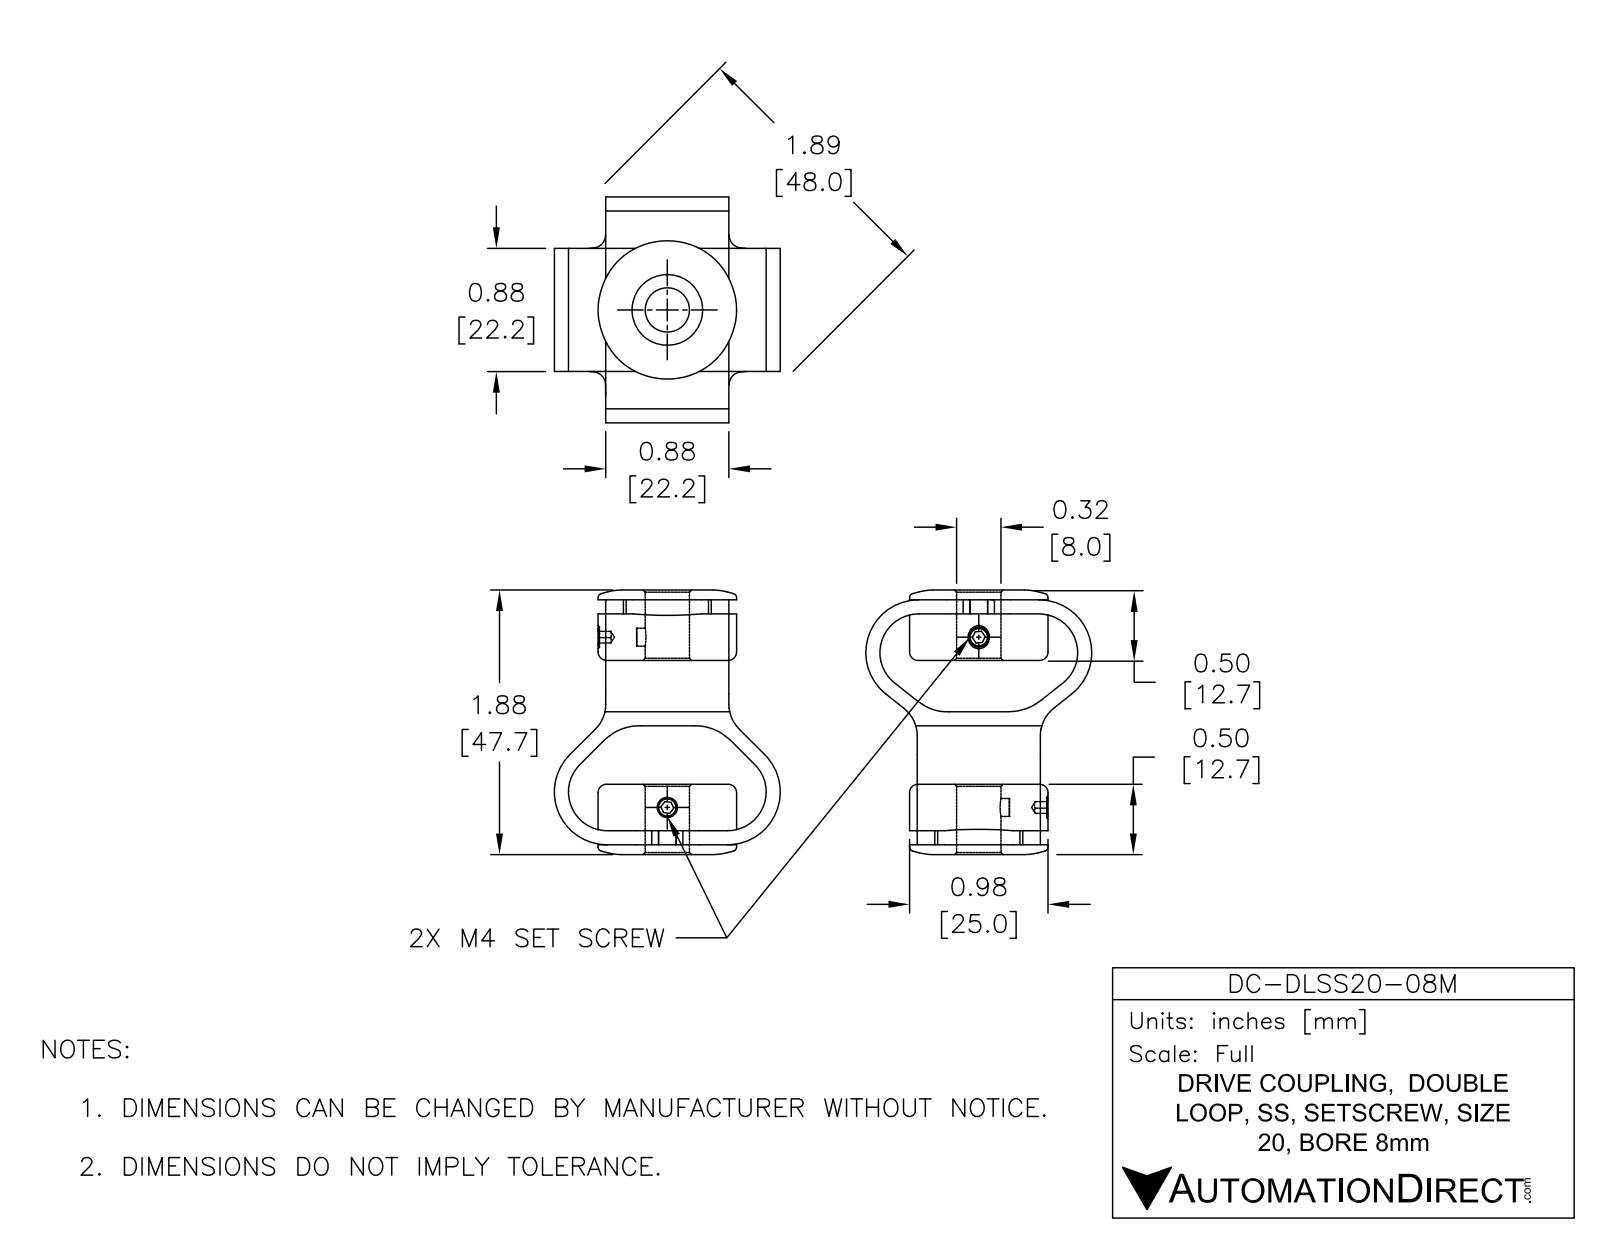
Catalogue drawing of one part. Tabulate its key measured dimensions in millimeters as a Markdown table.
| quantity | value |
| --- | --- |
| part name | DC-DLSS20-08M |
| STEP written by | SolidWorks 2015 (AUTOMOTIVE_DESIGN) |
| units | millimeters |
| bodies | 1 solid, 173 faces (90 planar, 47 cylindrical, 36 other) |
| overall size | 47.75 × 40.77 × 40.77 |
| volume | 18 164 mm³ |
| surface area | 11 304 mm² |
| round holes (diameter × count) | 3.24 × 2, 8 × 1 |
| round bosses / shafts (diameter × count) | 25 × 1 |
| partial cylindrical surfaces (radius × count) | 9.53 × 7, 6.35 × 6, 6.99 × 4, 1.91 × 3, 1.91 × 1, 7.94 × 1 |
| main face-to-face distances | 2.54, 12.7, 35.05, 22.35, 13.08, 9.27, 1.78, 45.97, 10.92, 33.27 |
